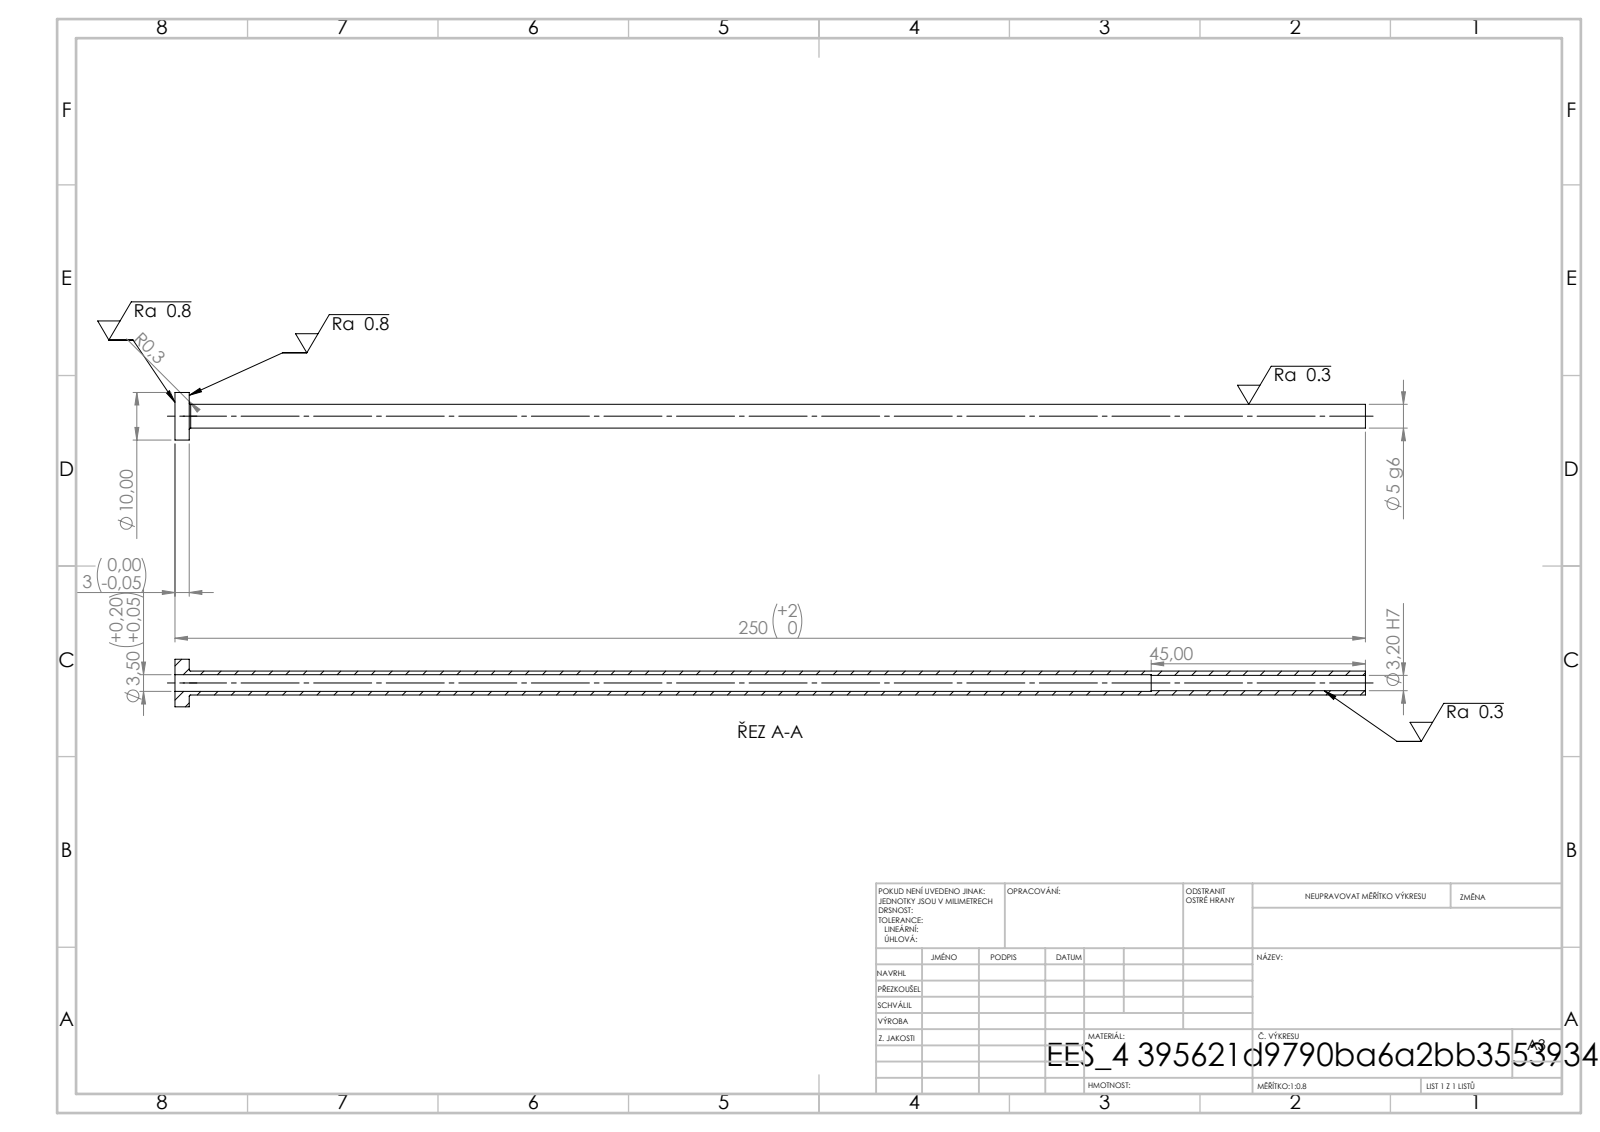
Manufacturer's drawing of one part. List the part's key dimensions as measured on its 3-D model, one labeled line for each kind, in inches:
STEP written by: SolidWorks 2019 (CONFIG_CONTROL_DESIGN)
Units: inches
Bodies: 1 solid, 14 faces (4 planar, 8 cylindrical, 2 other)
Overall size (bounding box): 9.843 × 0.394 × 0.394
Volume: 0.168 in³ · Surface area: 10.57 in²
Round holes (diameter × count): ⌀0.126 ×1, ⌀0.138 ×1
Round bosses / shafts (diameter × count): ⌀0.394 ×1, ⌀0.197 ×1
Main face-to-face distances: 0.118, 9.843, 9.724, 8.071, 7.953, 1.772
